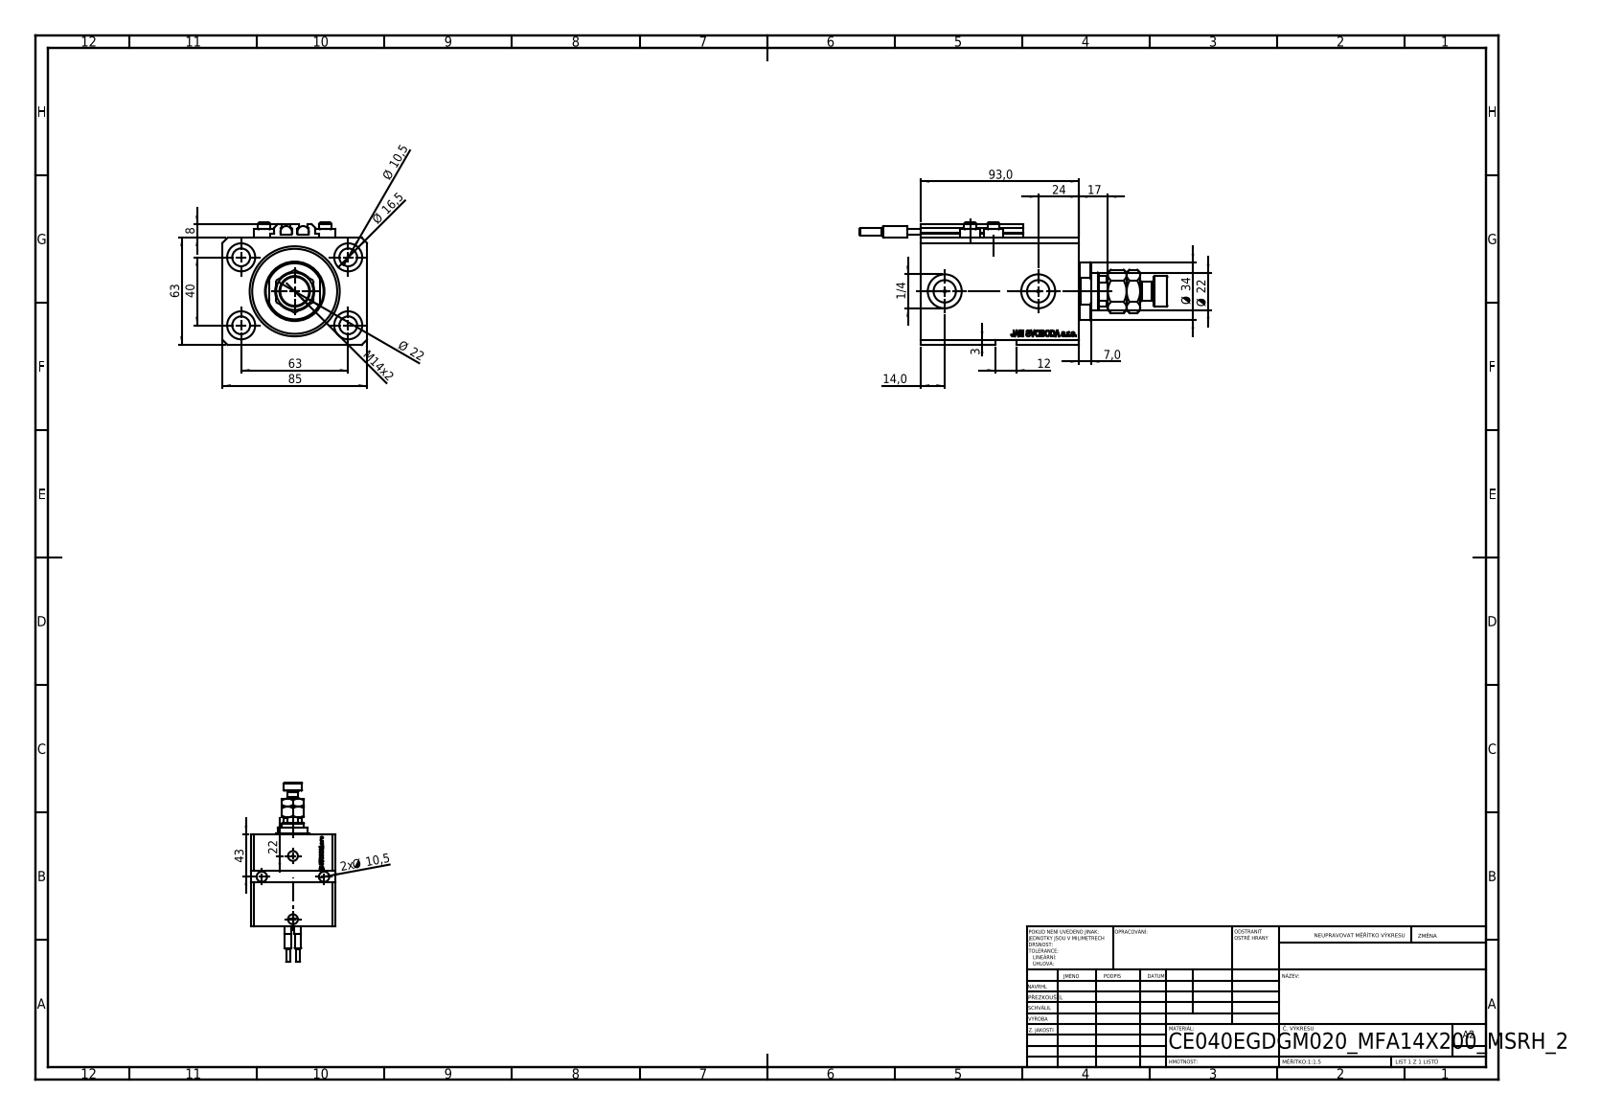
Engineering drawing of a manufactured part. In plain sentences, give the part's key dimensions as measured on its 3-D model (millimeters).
The part is named "MFA; SWITCH_V250CE; V250CE_C_VCP; V250CE_E_Body (+2 more)". Its 3-D file was written by "SolidWorks 2019 (CONFIG_CONTROL_DESIGN)". It is 11 solids with 1207 faces: 587 planar, 154 cylindrical and 466 other. Overall it measures 181 by 85 by 72 millimeters. Its volume is 447 891 cubic millimeters and its surface area 102 924 square millimeters. Round holes: 6 of diameter 10.5, 4 of diameter 1.25, 4 of diameter 4, 4 of diameter 16.5, 2 of diameter 10, 2 of diameter 13.16, 2 of diameter 20, 1 of diameter 12.5, 1 of diameter 22, 1 of diameter 40, 1 of diameter 53. Round bosses or shafts: 4 of diameter 11.6, 4 of diameter 7, 2 of diameter 6.8, 2 of diameter 6.5, 2 of diameter 4, 1 of diameter 34, 1 of diameter 18, 1 of diameter 11. Partial cylindrical surfaces (rounded edges, fillets, slot ends): 10 of radius 0.2, 1 of radius 10.5. The main face-to-face distances are 63, 85, 93, 17, 76, 11.4, 64.6, 81.6, 65, 3. The hole center spacings are 37.31, 63, 13.6, 15.4, 24.96, 28.02, 28.43, 33.62.
